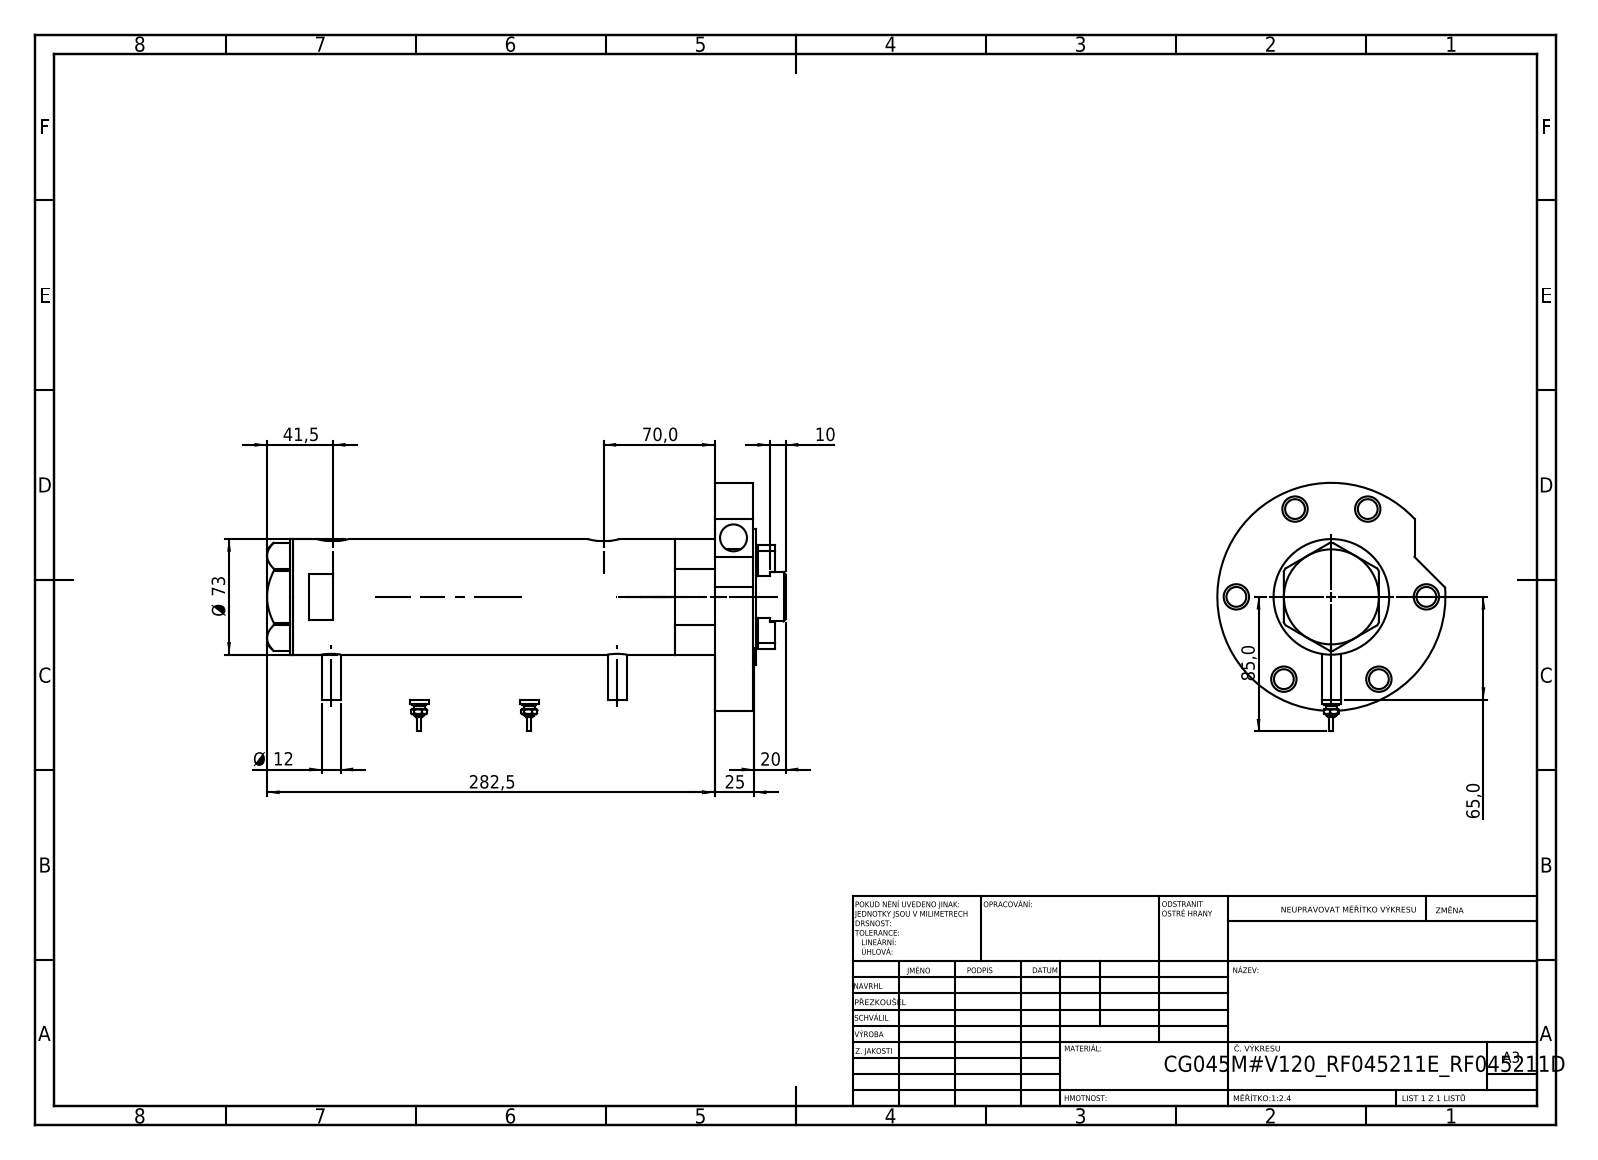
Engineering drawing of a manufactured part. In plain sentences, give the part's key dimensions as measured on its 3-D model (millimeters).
The part is named "V270CG_VC; V270CG_RF211D; V270CG_MIDDLE; V270CG_BACK (+3 more)". Its 3-D file was written by "SolidWorks 2019 (CONFIG_CONTROL_DESIGN)". It is 9 solids with 296 faces: 112 planar, 120 cylindrical and 64 other. Overall it measures 327.5 by 157 by 144 millimeters. Its volume is 1 432 000 cubic millimeters and its surface area 245 634 square millimeters. Round holes: 8 of diameter 12.5, 6 of diameter 16, 4 of diameter 8.1, 4 of diameter 13.5, 2 of diameter 13.16, 1 of diameter 10.5, 1 of diameter 17, 1 of diameter 32, 1 of diameter 33.5, 1 of diameter 45, 1 of diameter 48, 1 of diameter 60. Round bosses or shafts: 4 of diameter 12, 2 of diameter 9, 2 of diameter 7, 2 of diameter 4.5, 2 of diameter 2.5, 1 of diameter 144, 1 of diameter 86, 1 of diameter 73. Partial cylindrical surfaces (rounded edges, fillets, slot ends): 2 of radius 10. The main face-to-face distances are 24, 266, 26, 2, 290, 292, 1, 196, 70, 94. The hole center spacings are 60, 25.14, 57.72, 71.64, 15, 35.04, 35.9, 43.78.
